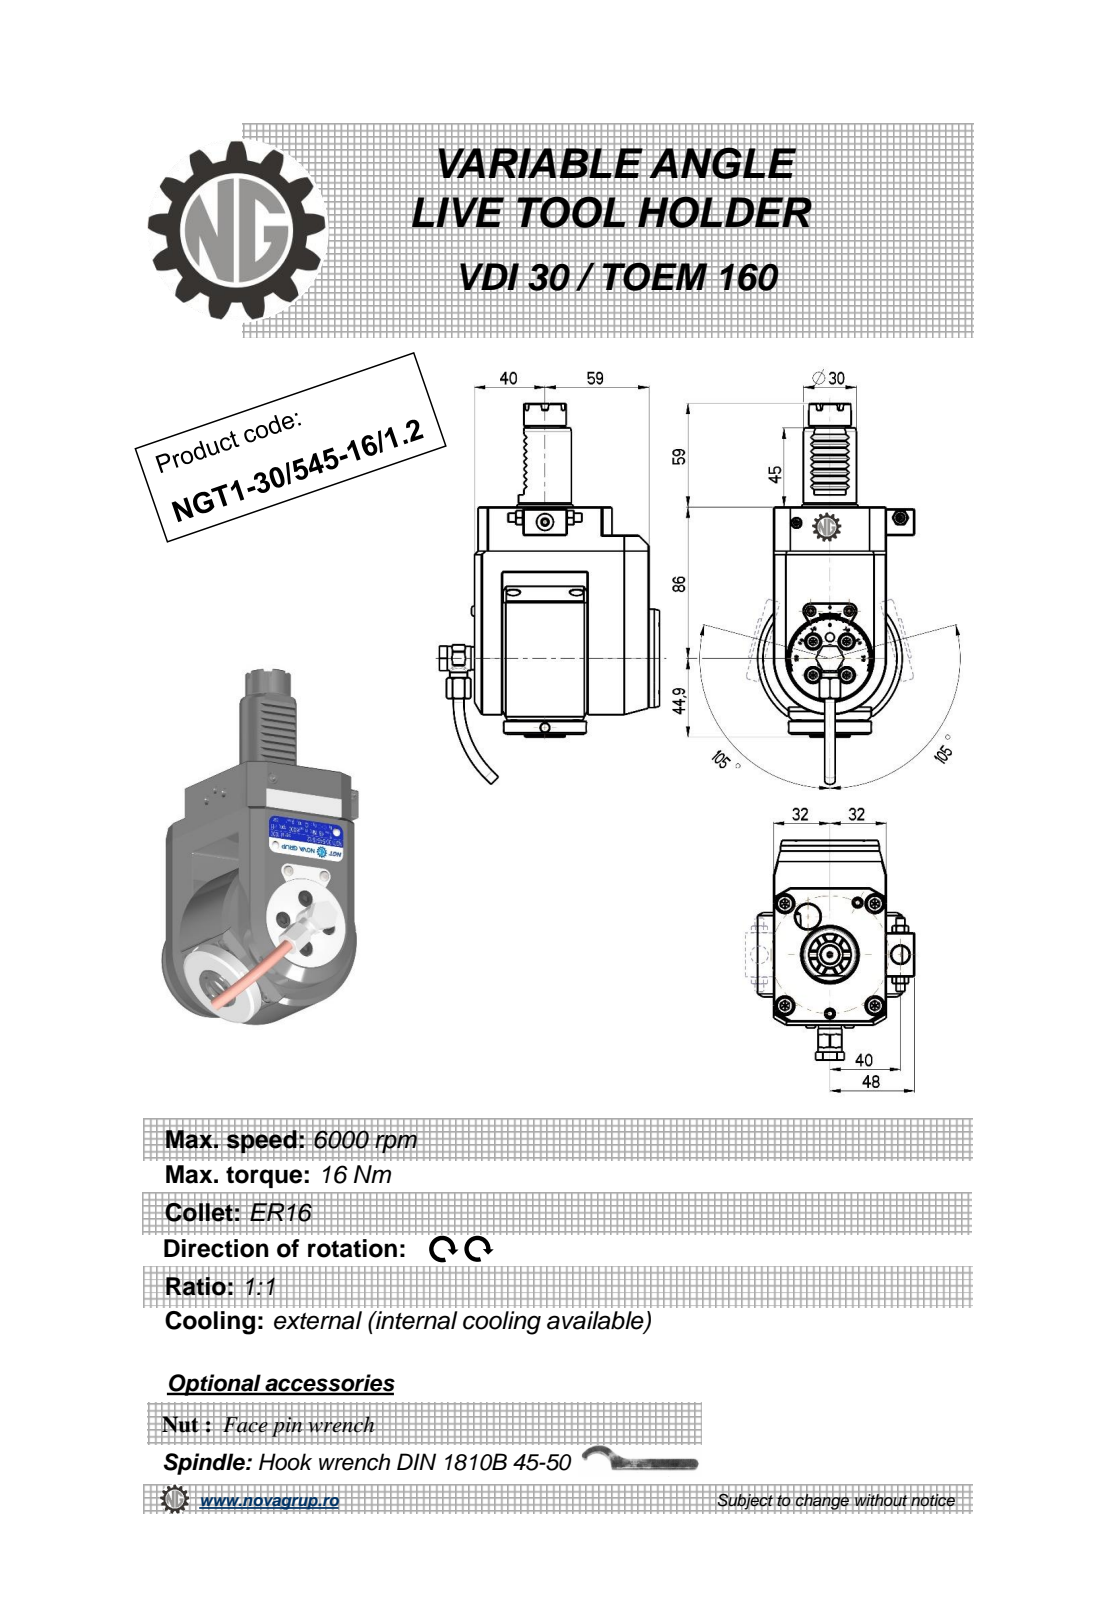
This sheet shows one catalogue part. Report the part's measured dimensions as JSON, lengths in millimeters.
{"part_name": "NGT1_30_545_16_1_2", "step_written_by": "PRO/ENGINEER BY PARAMETRIC TECHNOLOGY CORPORATION, 2010280 (CONFIG_CONTROL_DESIGN)", "units": "millimeters", "bodies": {"solids": 1, "faces": 510, "planar": 217, "cylindrical": 134, "other": 159}, "overall_size": [216.67, 124.9, 89], "volume_mm3": 757563, "surface_area_mm2": 71617, "round_holes": [[3.2, 4], [4, 3], [5, 2], [10, 2], [3, 1], [4.2, 1], [4.5, 1], [6.2, 1], [9, 1], [9.5, 1], [11, 1], [12.5, 1]], "round_bosses_or_shafts": [[6, 2], [5.7, 2], [82, 1], [56, 1], [47, 1], [35, 1], [30, 1], [24, 1]], "partial_cylinders_radius": [[0.26, 12], [0.3, 8], [0.5, 4], [1, 2], [7.7, 1], [32, 1]], "face_to_face_distances": [64, 16, 37, 99, 6, 105, 83, 14, 62, 48], "hole_center_spacings": [9.25, 13.08, 18.5, 41.06, 49.87, 50.26, 0.4, 30.75]}
